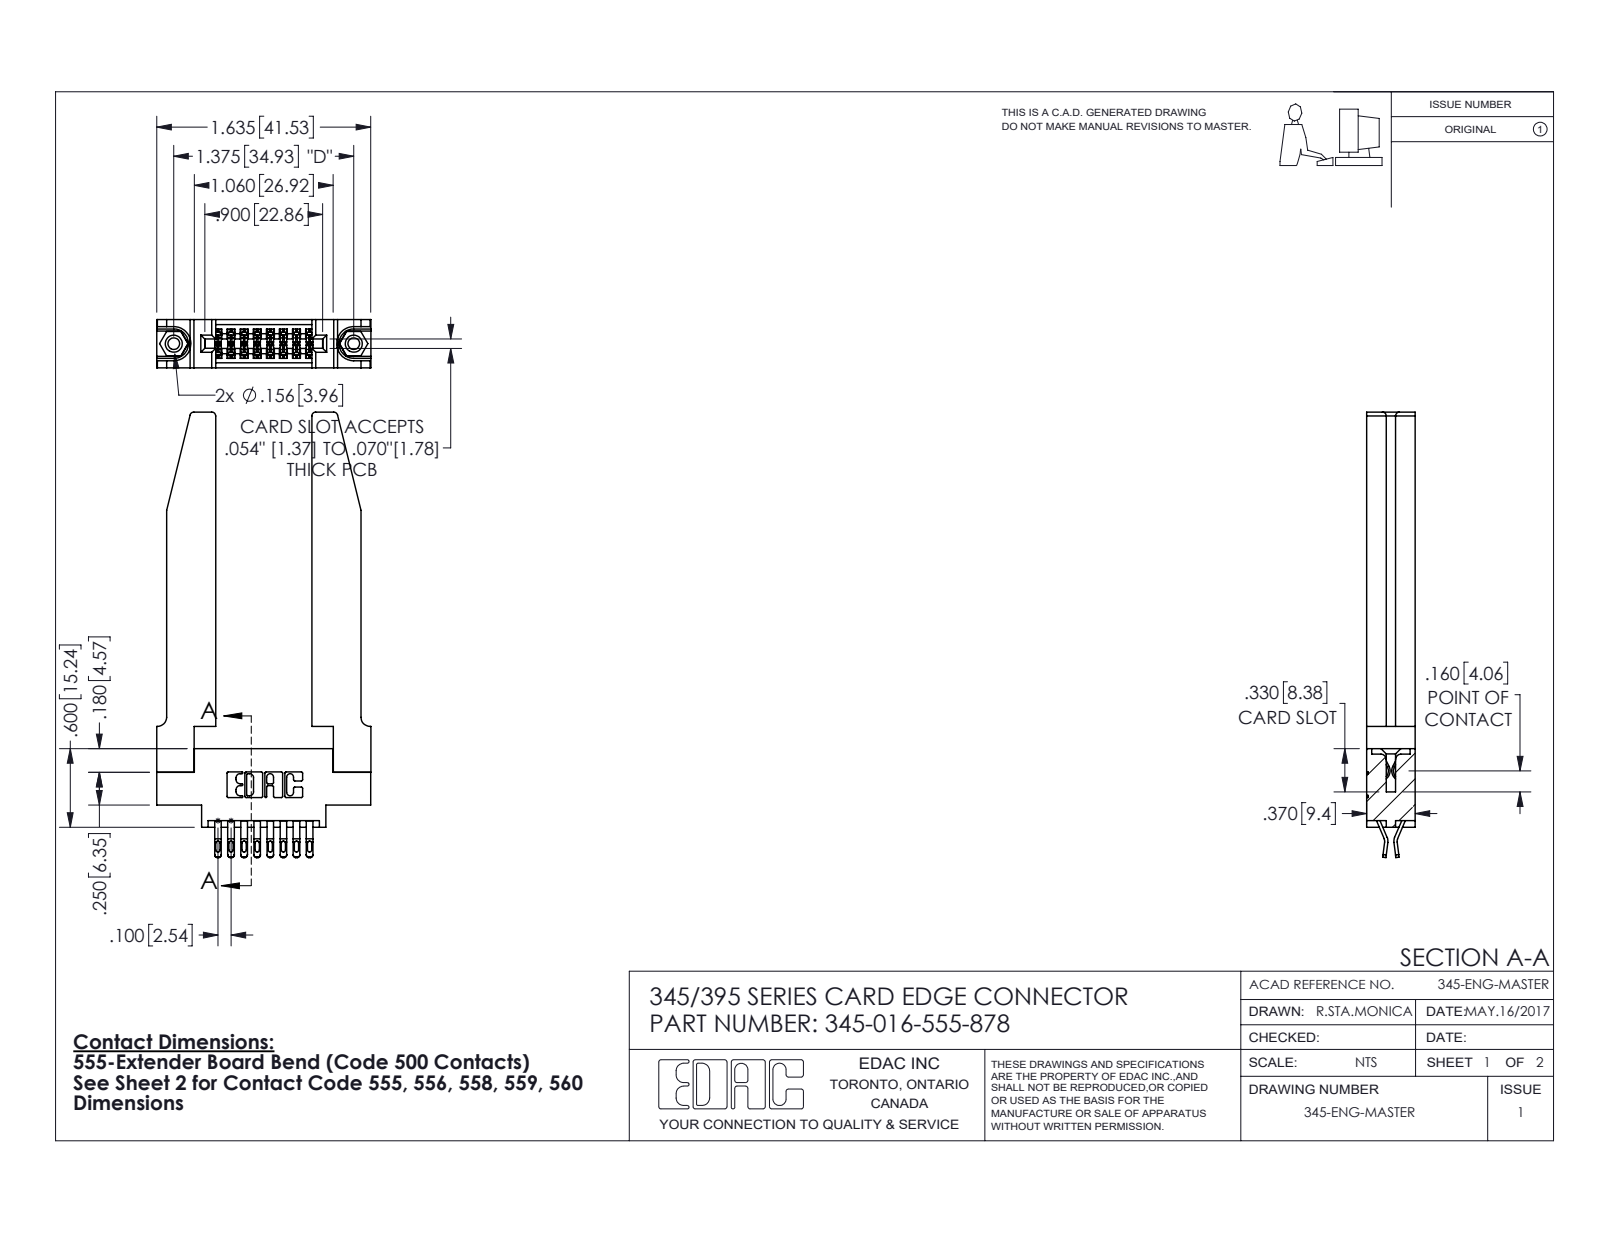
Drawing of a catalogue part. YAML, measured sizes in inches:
part_name: "345 Part_0.170 Offset - 0.156 Dia-TH; 345-292-001_555 Tail; 345-250-001_345-250-001-102; 345-220-078_345-220-078 (+1 more)"
step_written_by: "SolidWorks 2016 (CONFIG_CONTROL_DESIGN)"
units: inches
bodies: {solids: 21, faces: 1260, planar: 722, cylindrical: 486, other: 52}
overall_size: [3.402, 1.636, 0.37]
volume: 0.697
surface_area: 18.42
round_holes:
  - {diameter: 0.089, count: 2}
  - {diameter: 0.125, count: 2}
  - {diameter: 0.156, count: 2}
  - {diameter: 0.064, count: 1}
round_bosses_or_shafts:
  - {diameter: 0.155, count: 2}
partial_cylinders:
  - {radius: 0.016, count: 40}
  - {radius: 0.02, count: 32}
  - {radius: 0.006, count: 24}
  - {radius: 0.01, count: 22}
  - {radius: 0.03, count: 8}
  - {radius: 0.007, count: 6}
  - {radius: 0.031, count: 6}
  - {radius: 0.026, count: 3}
face_to_face_distances: [0.37, 0.072, 0.148, 0.15, 0.298, 0.22, 0.077, 0.735, 0.095, 0.025]
hole_center_spacings: [0.27, 1.144, 1.375]
